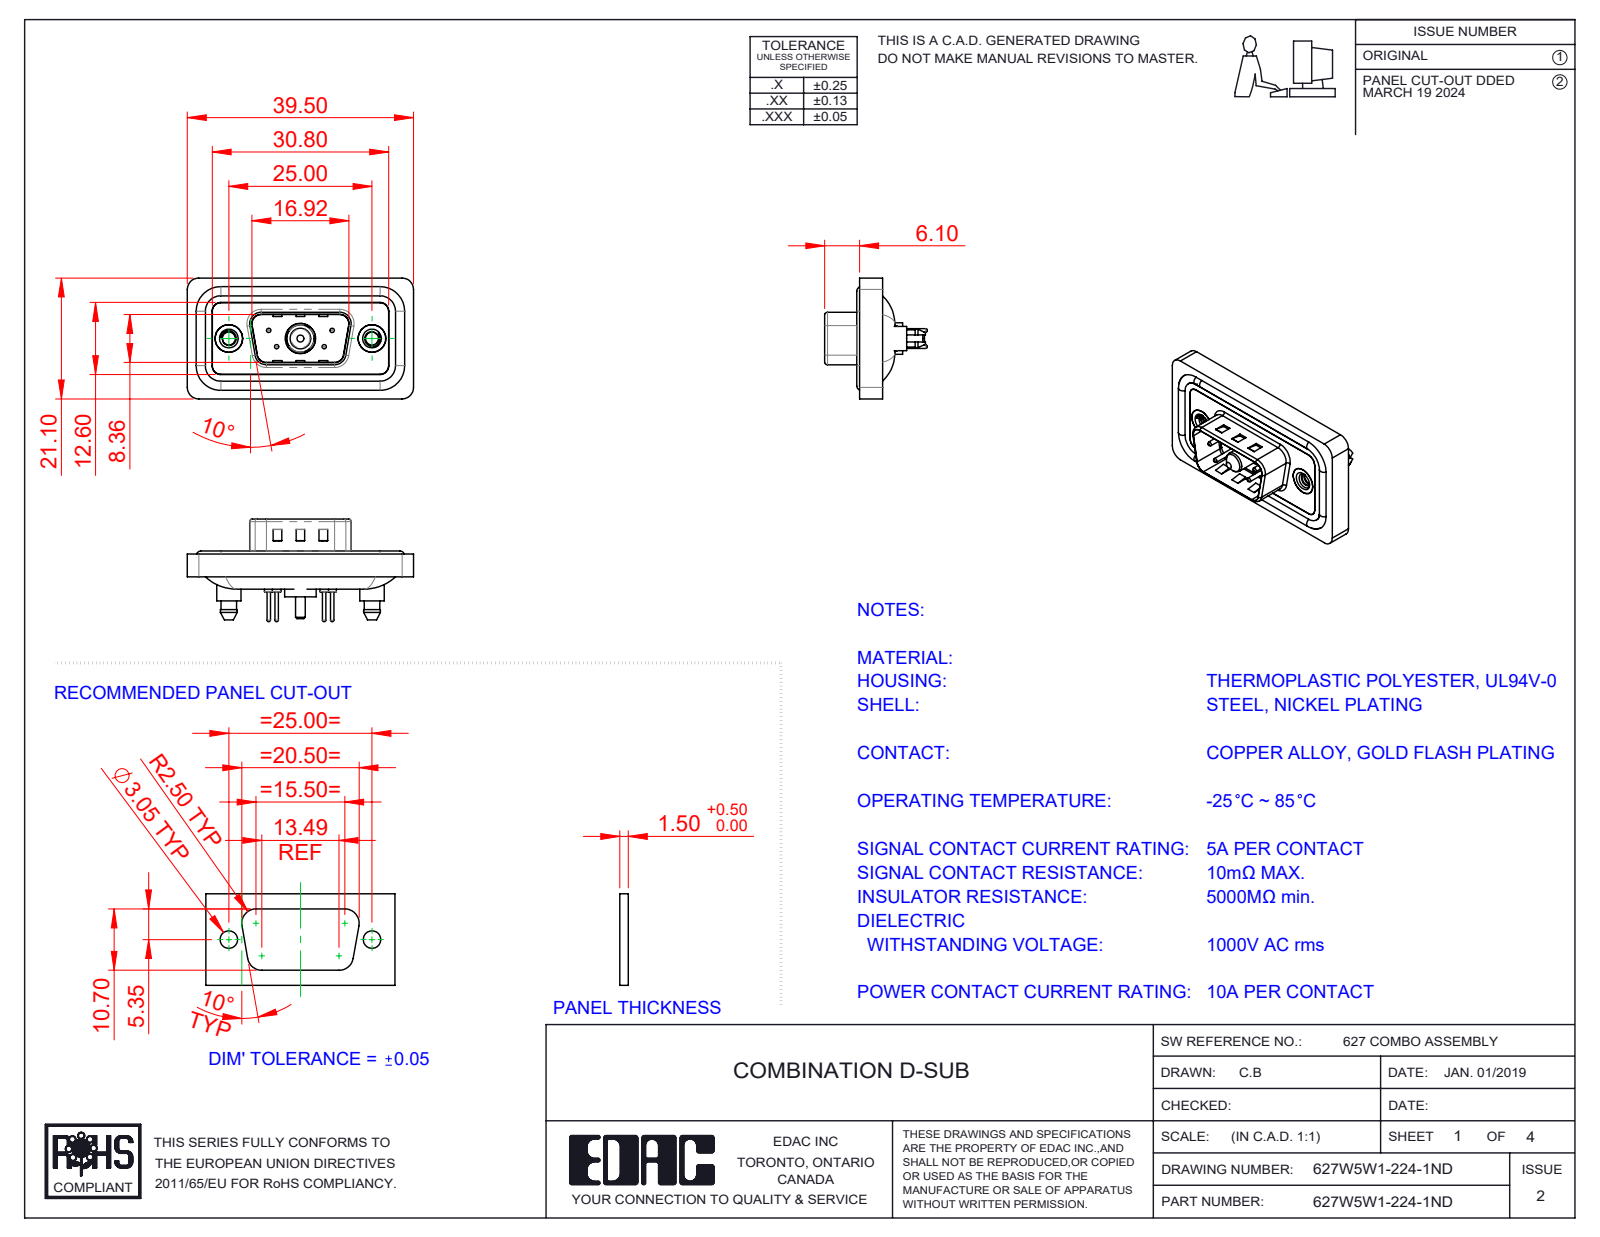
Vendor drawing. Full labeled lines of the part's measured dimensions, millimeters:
Part name (STEP PRODUCT): 627Combo Contact Row 2_24; 627Combo Threaded Boardlock_D; 627W5W1-224-1ND; 627Combo Shell Front_09 Contacts (+6 more)
STEP written by: SolidWorks 2023 (CONFIG_CONTROL_DESIGN)
Units: millimetres
Bodies: 13 solids, 656 faces (199 planar, 295 cylindrical, 162 other)
Overall size (bounding box): 39.5 × 21.1 × 17.9
Volume: 4 507 mm³ · Surface area: 7 265 mm²
Round holes (diameter × count): ⌀0.75 ×4, ⌀1.6 ×4, ⌀2 ×4, ⌀2.26 ×2, ⌀4 ×2, ⌀4.8 ×2, ⌀5 ×2, ⌀4.85 ×1, ⌀5.3 ×1
Round bosses / shafts (diameter × count): ⌀1.6 ×4, ⌀1.5 ×4, ⌀0.6 ×4, ⌀5.4 ×2, ⌀4.9 ×2, ⌀4.25 ×2, ⌀5.5 ×1, ⌀5.2 ×1
Partial cylindrical surfaces — rounded edges, fillets, slot ends (radius × count): R1.5 ×24, R2 ×18, R1.6 ×10, R0.5 ×8, R0.25 ×4, R0.6 ×4, R0.65 ×4, R0.9 ×4
Main face-to-face distances: 0.4, 1.1, 2.9, 1.6, 1.5, 3.1, 0.5, 2.5, 4, 0.7
Hole centre spacings: 3.16, 5.72, 7.1, 12.5, 18.1, 4.39, 4.4, 8.31
